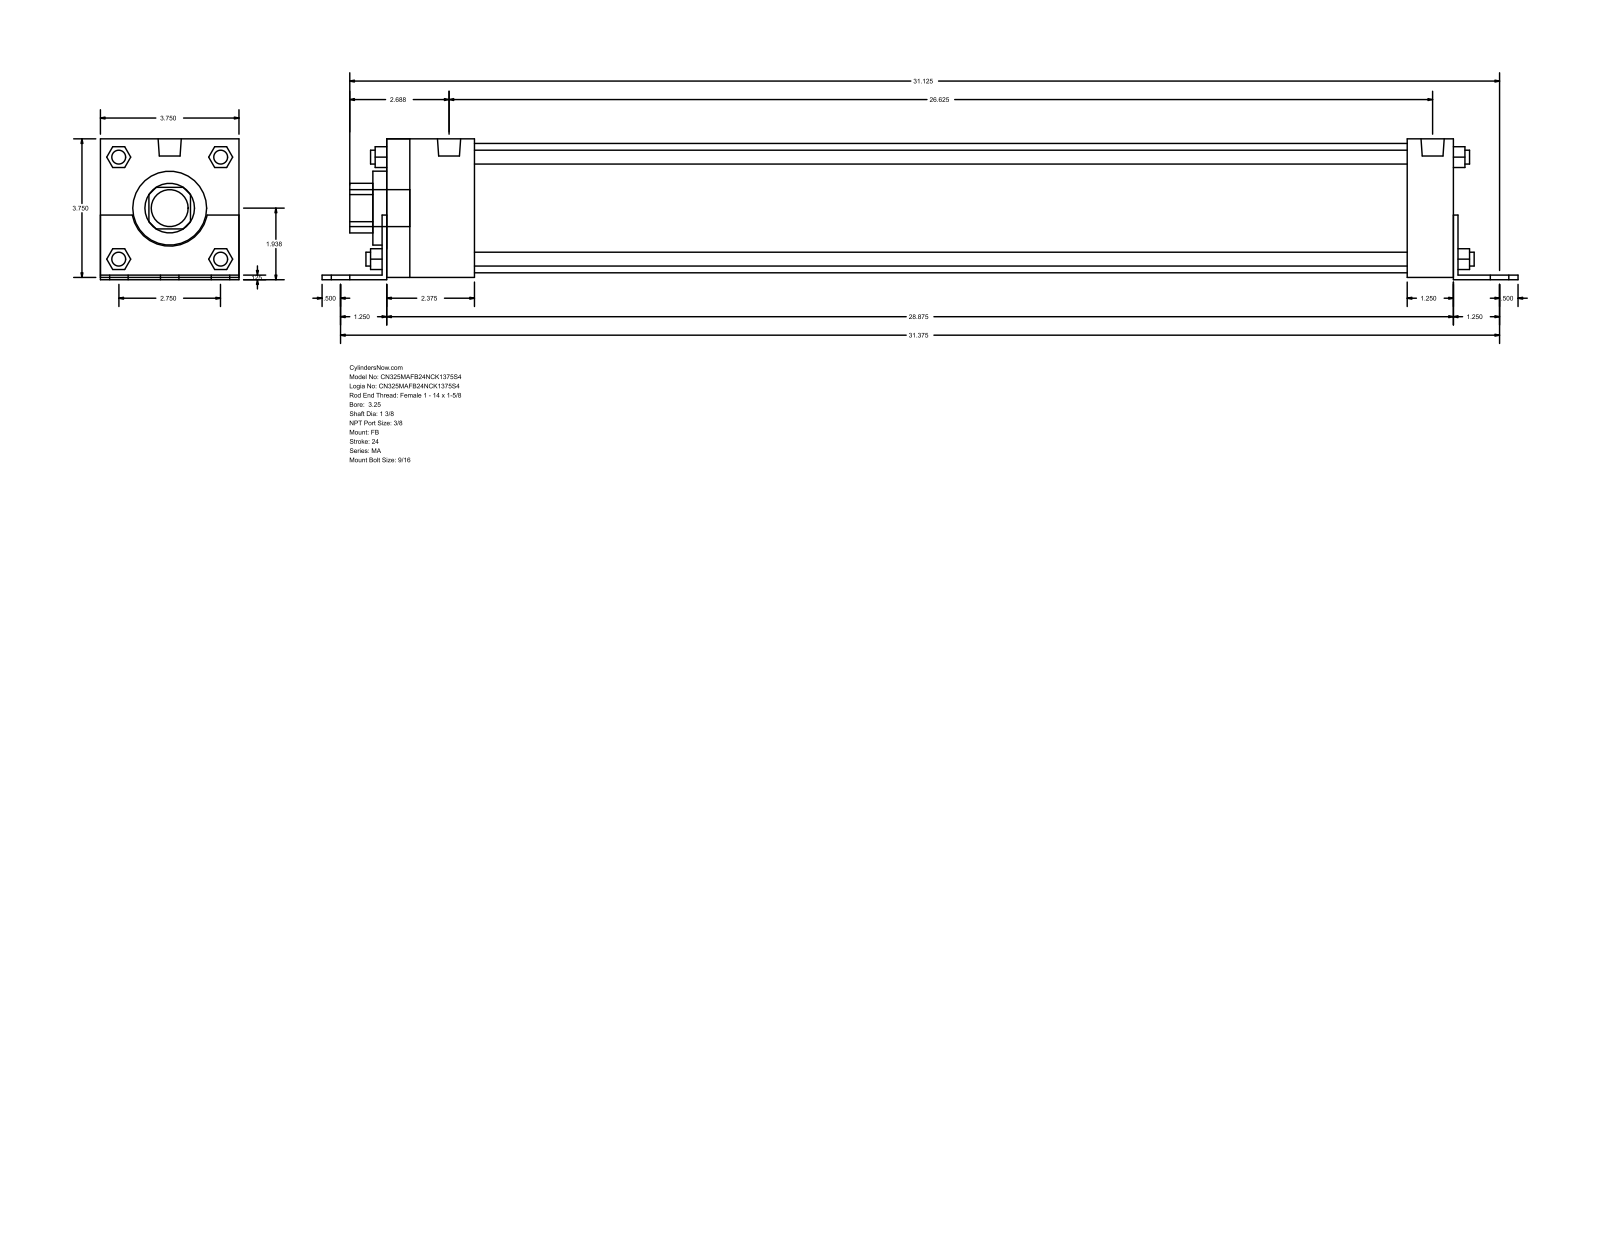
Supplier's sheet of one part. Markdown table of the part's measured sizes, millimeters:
| quantity | value |
| --- | --- |
| part name | MA_FB__0325_1.375 |
| STEP written by | GSSL Pune (CONFIG_CONTROL_DESIGN) |
| units | millimeters |
| bodies | 0 solids, 140 faces (105 planar, 35 cylindrical, 0 other) |
| overall size | 822.33 × 96.84 × 95.25 |
| round holes (diameter × count) | 34.92 × 1, 50.8 × 1, 88.9 × 1 |
| round bosses / shafts (diameter × count) | 14.29 × 6, 11.11 × 4, 9.53 × 4, 15.93 × 2, 25.4 × 1 |
| partial cylindrical surfaces (radius × count) | 17.06 × 1, 26.16 × 1 |
| main face-to-face distances | 95.24, 3.17, 1.59, 96.83, 1.58, 93.66, 736.6, 733.43, 31.75, 60.32 |
